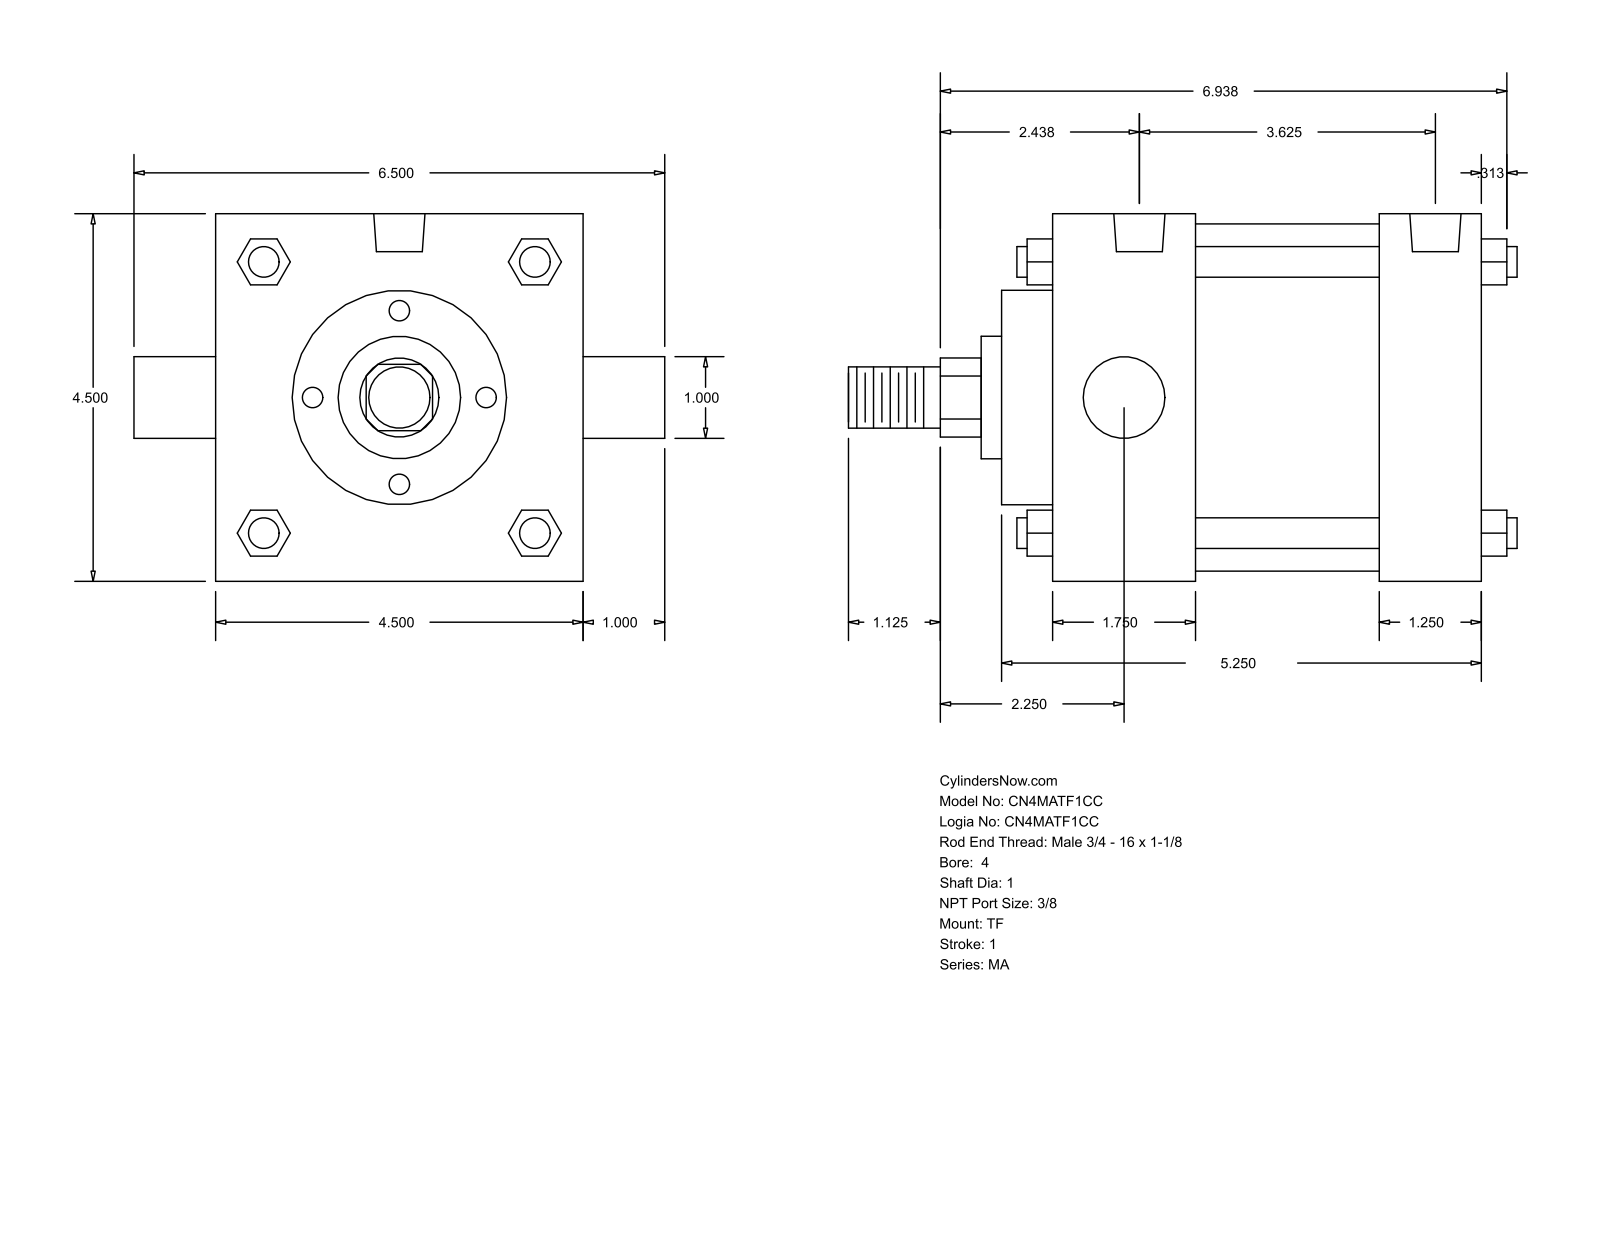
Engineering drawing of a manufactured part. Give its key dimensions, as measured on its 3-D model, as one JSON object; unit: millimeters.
{"part_name": "MA_TF__0400_1", "step_written_by": "GSSL Pune (CONFIG_CONTROL_DESIGN)", "units": "millimeters", "bodies": {"solids": 0, "faces": 122, "planar": 93, "cylindrical": 29, "other": 0}, "overall_size": [207.96, 165.1, 114.3], "round_holes": [[11.11, 3], [15.93, 2]], "round_bosses_or_shafts": [[9.53, 4], [25.4, 2], [107.95, 1], [66.67, 1], [38.1, 1], [19.05, 1]], "partial_cylinders_radius": [[12.29, 1]], "face_to_face_distances": [114.3, 133.36, 101.61, 31.75, 44.46, 57.15, 88.9, 15.87, 60.33, 117.48], "hole_center_spacings": [4.76, 4.77, 82.55, 87.31, 87.32, 92.08]}
